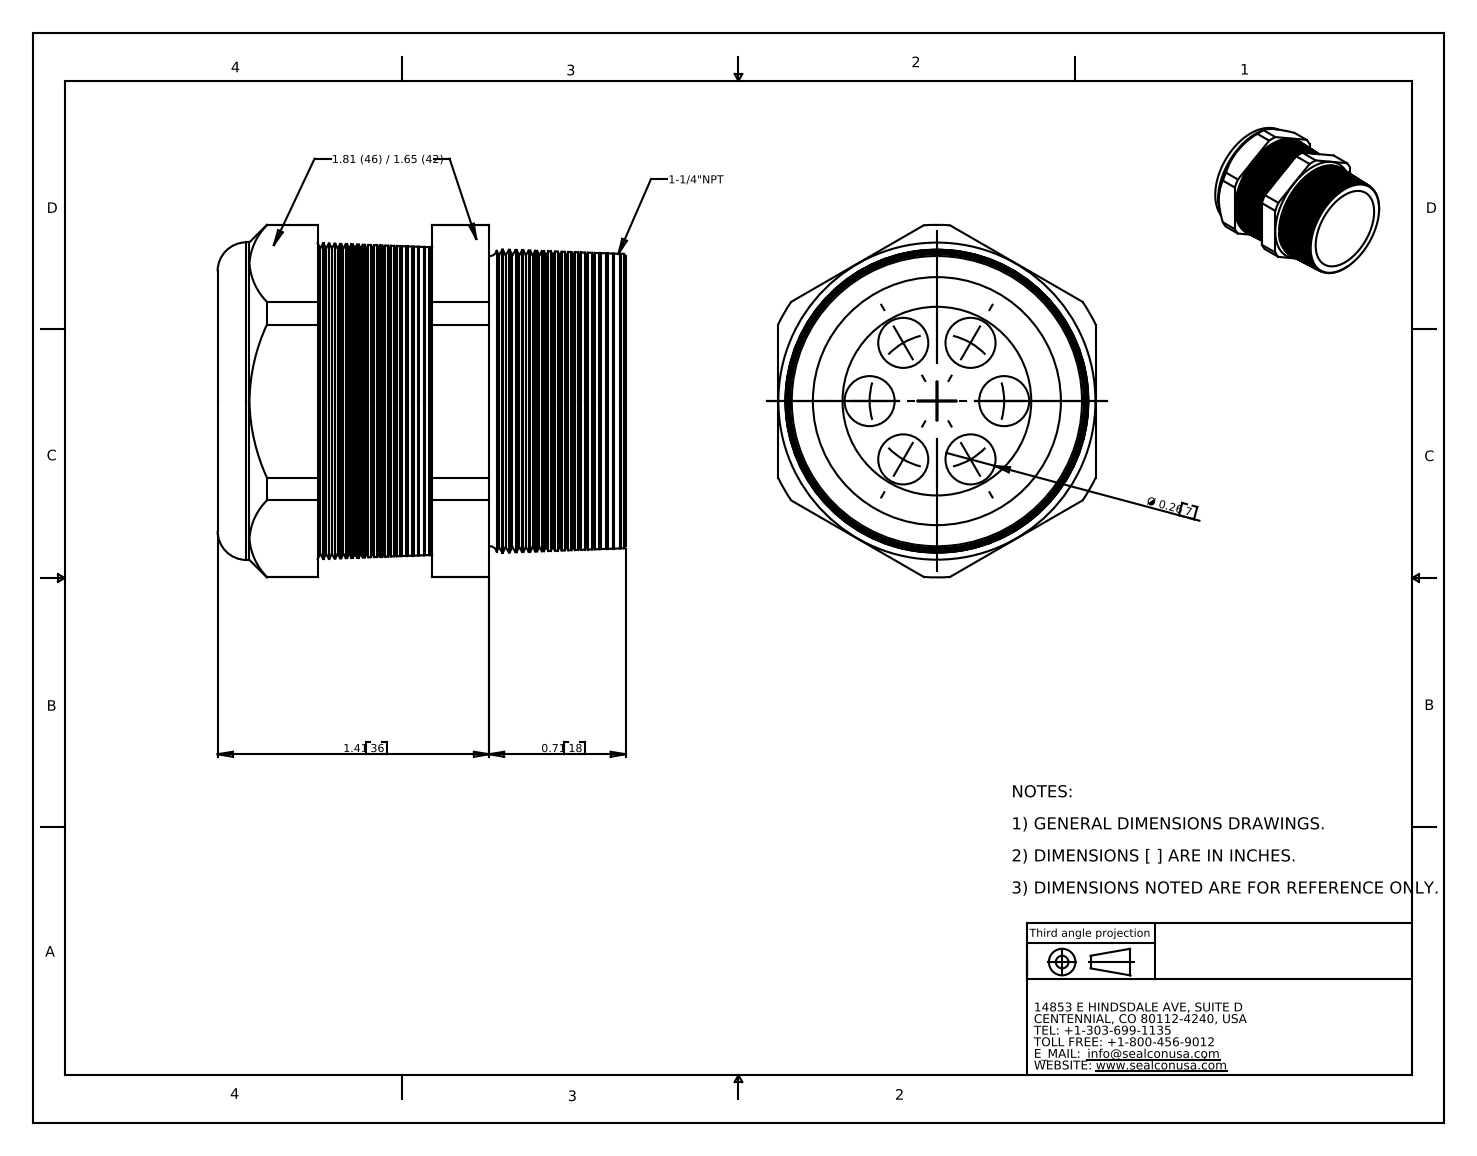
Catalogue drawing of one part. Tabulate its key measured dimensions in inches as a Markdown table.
| quantity | value |
| --- | --- |
| part name | CD29L1-GY |
| STEP written by | SolidWorks 2007 (CONFIG_CONTROL_DESIGN) |
| units | inches |
| bodies | 2 solids, 319 faces (21 planar, 32 cylindrical, 266 other) |
| overall size | 2.16 × 1.831 × 1.65 |
| volume | 2.602 in³ |
| surface area | 30.02 in² |
| round holes (diameter × count) | 0.26 × 6, 0.96 × 1, 0.98 × 1 |
| round bosses / shafts (diameter × count) | 1.65 × 1 |
| partial cylindrical surfaces (radius × count) | 0.916 × 1 |
| main face-to-face distances | 1.65, 1.65, 2.16, 0.5, 1.66, 0.02, 0.48, 2.14, 1.235, 1.215 |
| hole center spacings | 0.35, 0.606, 0.699 |
